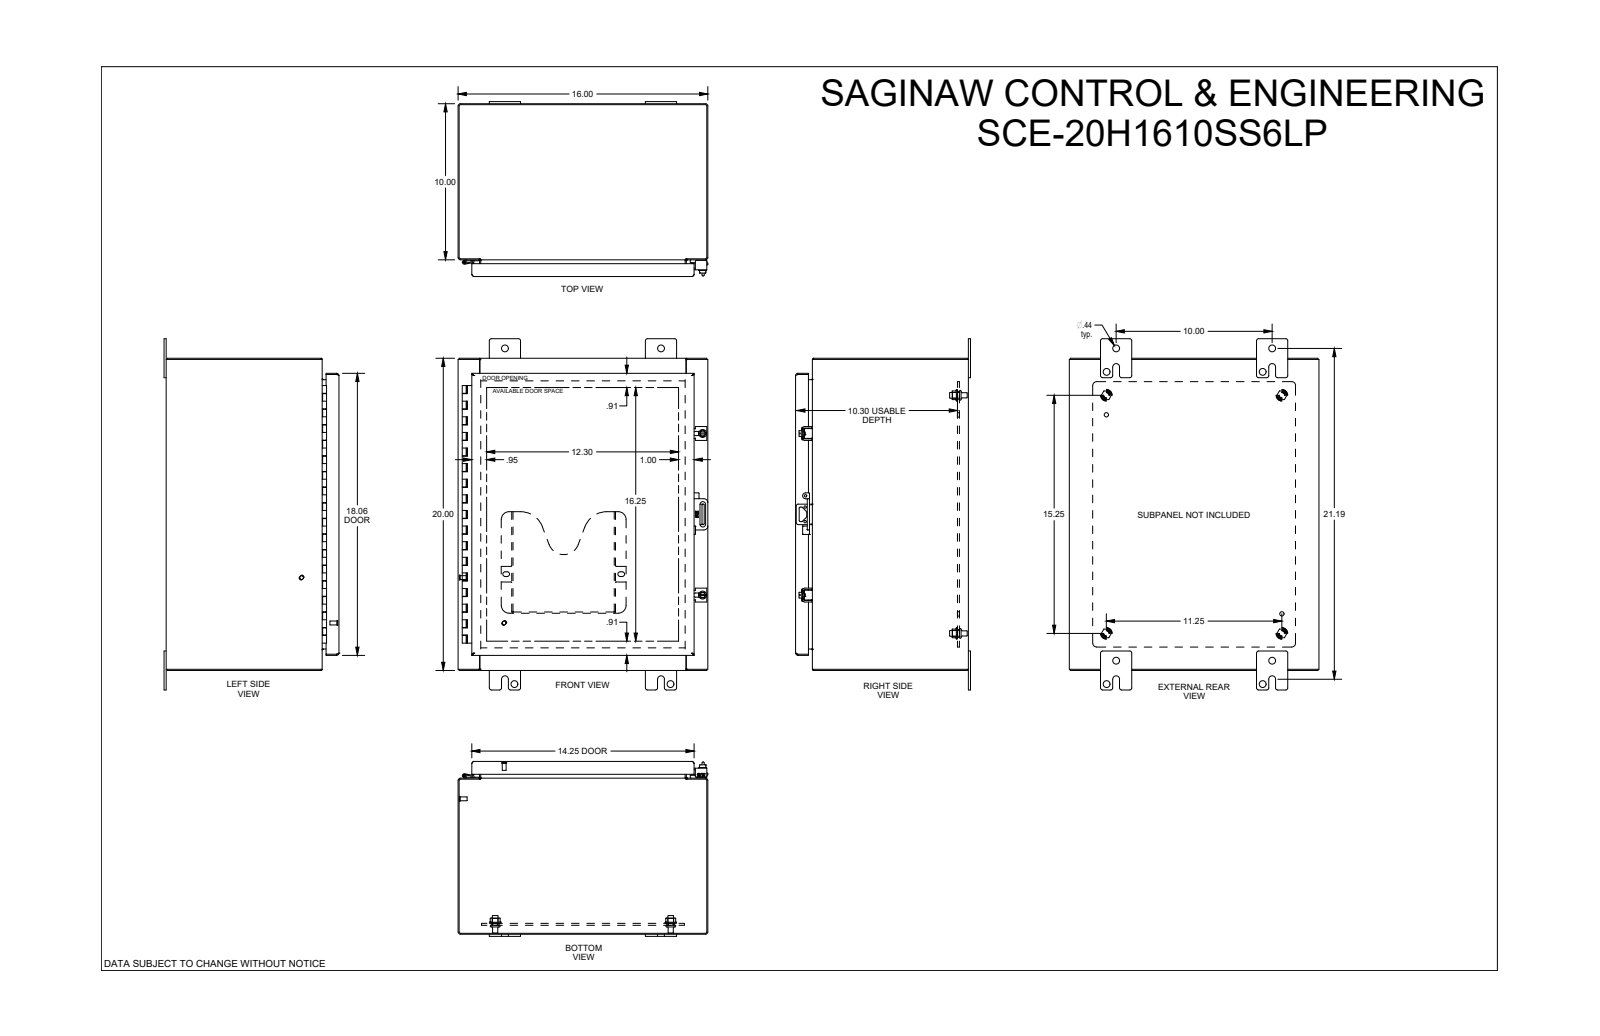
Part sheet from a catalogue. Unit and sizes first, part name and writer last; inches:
Units: inches
Overall size (bounding box): 22.5 × 16 × 11.343
Round holes (diameter × count): ⌀0.172 ×4, ⌀0.205 ×4, ⌀0.218 ×4, ⌀0.244 ×4, ⌀0.312 ×4, ⌀0.437 ×4, ⌀0.5 ×4, ⌀0.375 ×3, ⌀0.04 ×2, ⌀0.16 ×2, ⌀0.188 ×2, ⌀0.203 ×2
Round bosses / shafts (diameter × count): ⌀0.248 ×7, ⌀0.25 ×6, ⌀0.59 ×4, ⌀0.376 ×4, ⌀0.375 ×4, ⌀0.33 ×4, ⌀0.31 ×4, ⌀0.24 ×4
Partial cylindrical surfaces — rounded edges, fillets, slot ends (radius × count): R0.025 ×68, R0.01 ×62, R0.03 ×32, R0.06 ×26, R0.015 ×24, R0.185 ×21, R0.04 ×18, R0.22 ×16
Main face-to-face distances: 0.075, 15.925, 0.06, 10.993, 19.925, 11.068, 11.008, 10.933, 0.575, 0.5
Hole centre spacings: 16.887, 18.5, 1.375, 1.741, 1.741, 2.942, 4.916, 9.999
Volume: 157.1 in³ · Surface area: 3 774 in²
Bodies: 37 solids, 1912 faces (740 planar, 798 cylindrical, 374 other)
Part name (STEP PRODUCT): SCE-20H1610LP
STEP written by: SolidWorks 2021 (AUTOMOTIVE_DESIGN)
